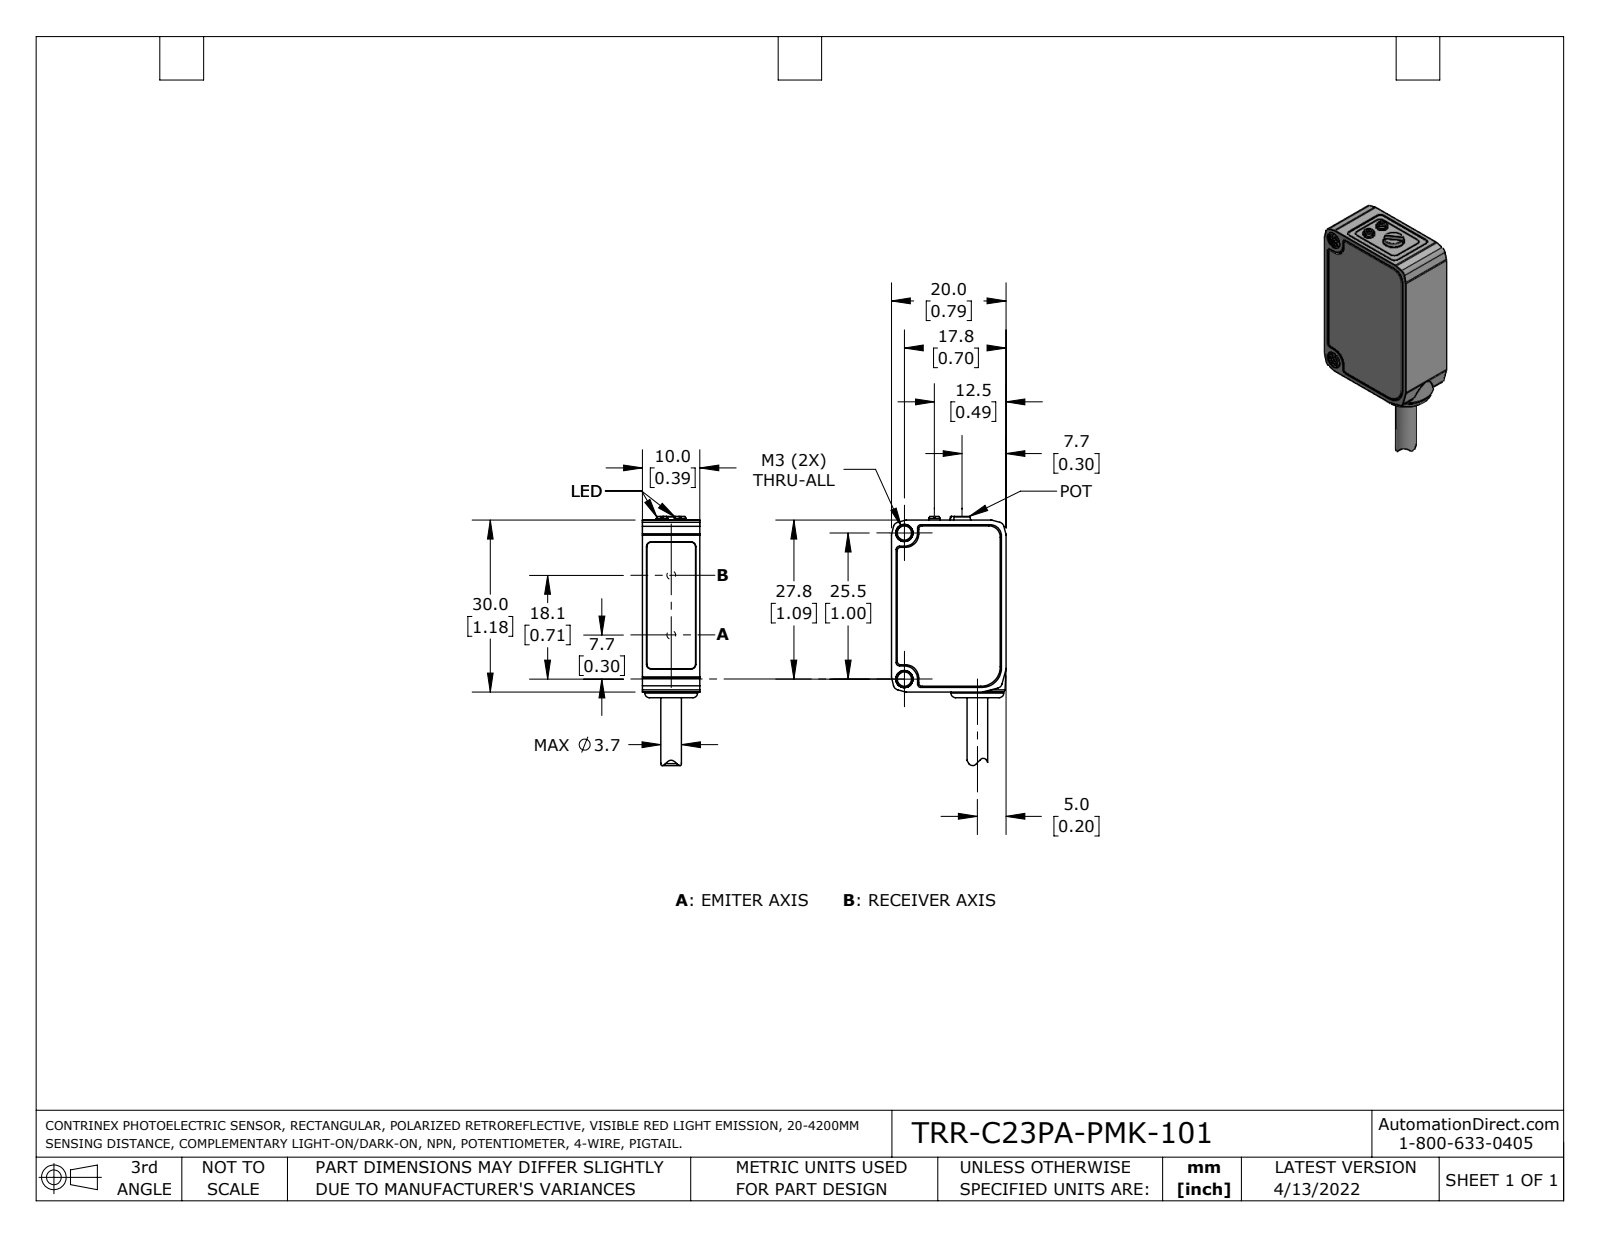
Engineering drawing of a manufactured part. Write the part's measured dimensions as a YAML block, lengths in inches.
part_name: "TRR-C23PA-PMK-101"
step_written_by: "SolidWorks 2021 (AUTOMOTIVE_DESIGN)"
units: inches
bodies: {solids: 1, faces: 274, planar: 91, cylindrical: 136, other: 47}
overall_size: [1.713, 0.787, 0.394]
volume: 0.365
surface_area: 4.153
round_holes:
  - {diameter: 0.098, count: 2}
  - {diameter: 0.142, count: 2}
round_bosses_or_shafts:
  - {diameter: 0.079, count: 2}
  - {diameter: 0.362, count: 1}
  - {diameter: 0.146, count: 1}
  - {diameter: 0.142, count: 1}
partial_cylinders:
  - {radius: 0.031, count: 20}
  - {radius: 0.039, count: 11}
  - {radius: 0.024, count: 8}
  - {radius: 0.091, count: 4}
  - {radius: 0.134, count: 3}
  - {radius: 0.079, count: 2}
  - {radius: 0.025, count: 1}
  - {radius: 0.033, count: 1}
face_to_face_distances: [0.394, 0.785, 0.039, 0.787, 1.181, 1.177, 0.028, 0.03, 1.179, 1.217]
hole_center_spacings: [1.004]
